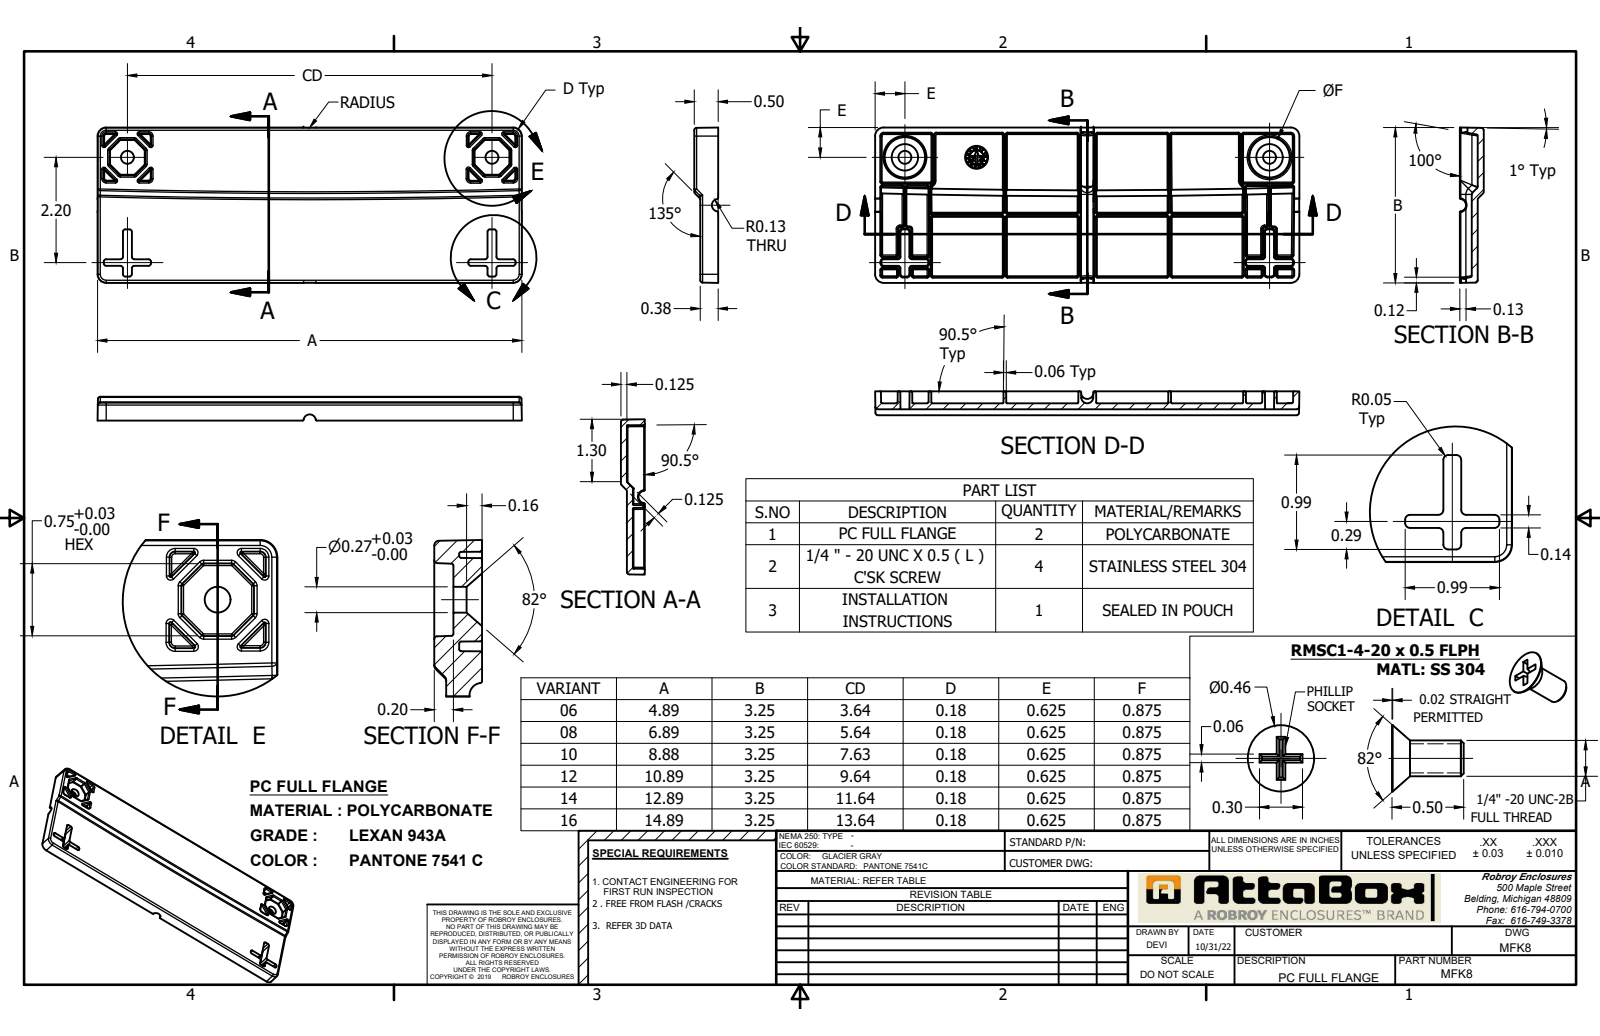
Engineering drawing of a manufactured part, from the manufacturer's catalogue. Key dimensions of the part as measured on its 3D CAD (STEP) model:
Part name (STEP PRODUCT): MFK8_Default
STEP written by: SolidWorks 2023 (CONFIG_CONTROL_DESIGN)
Units: inches
Bodies: 1 solid, 1195 faces (334 planar, 397 cylindrical, 464 other)
Overall size (bounding box): 6.89 × 3.25 × 0.5
Volume: 4.292 in³ · Surface area: 76.89 in²
Round holes (diameter × count): ⌀0.27 ×2
Partial cylindrical surfaces — rounded edges, fillets, slot ends (radius × count): R0.02 ×122, R0.03 ×117, R0.05 ×6, R0.125 ×3, R0.12 ×1, R0.129 ×1, R0.129 ×1, R0.13 ×1
Main face-to-face distances: 0.25, 0.125, 0.125, 0.5, 0.375, 1.069, 2.454, 1.385, 0.2, 0.075
Hole centre spacings: 5.64
